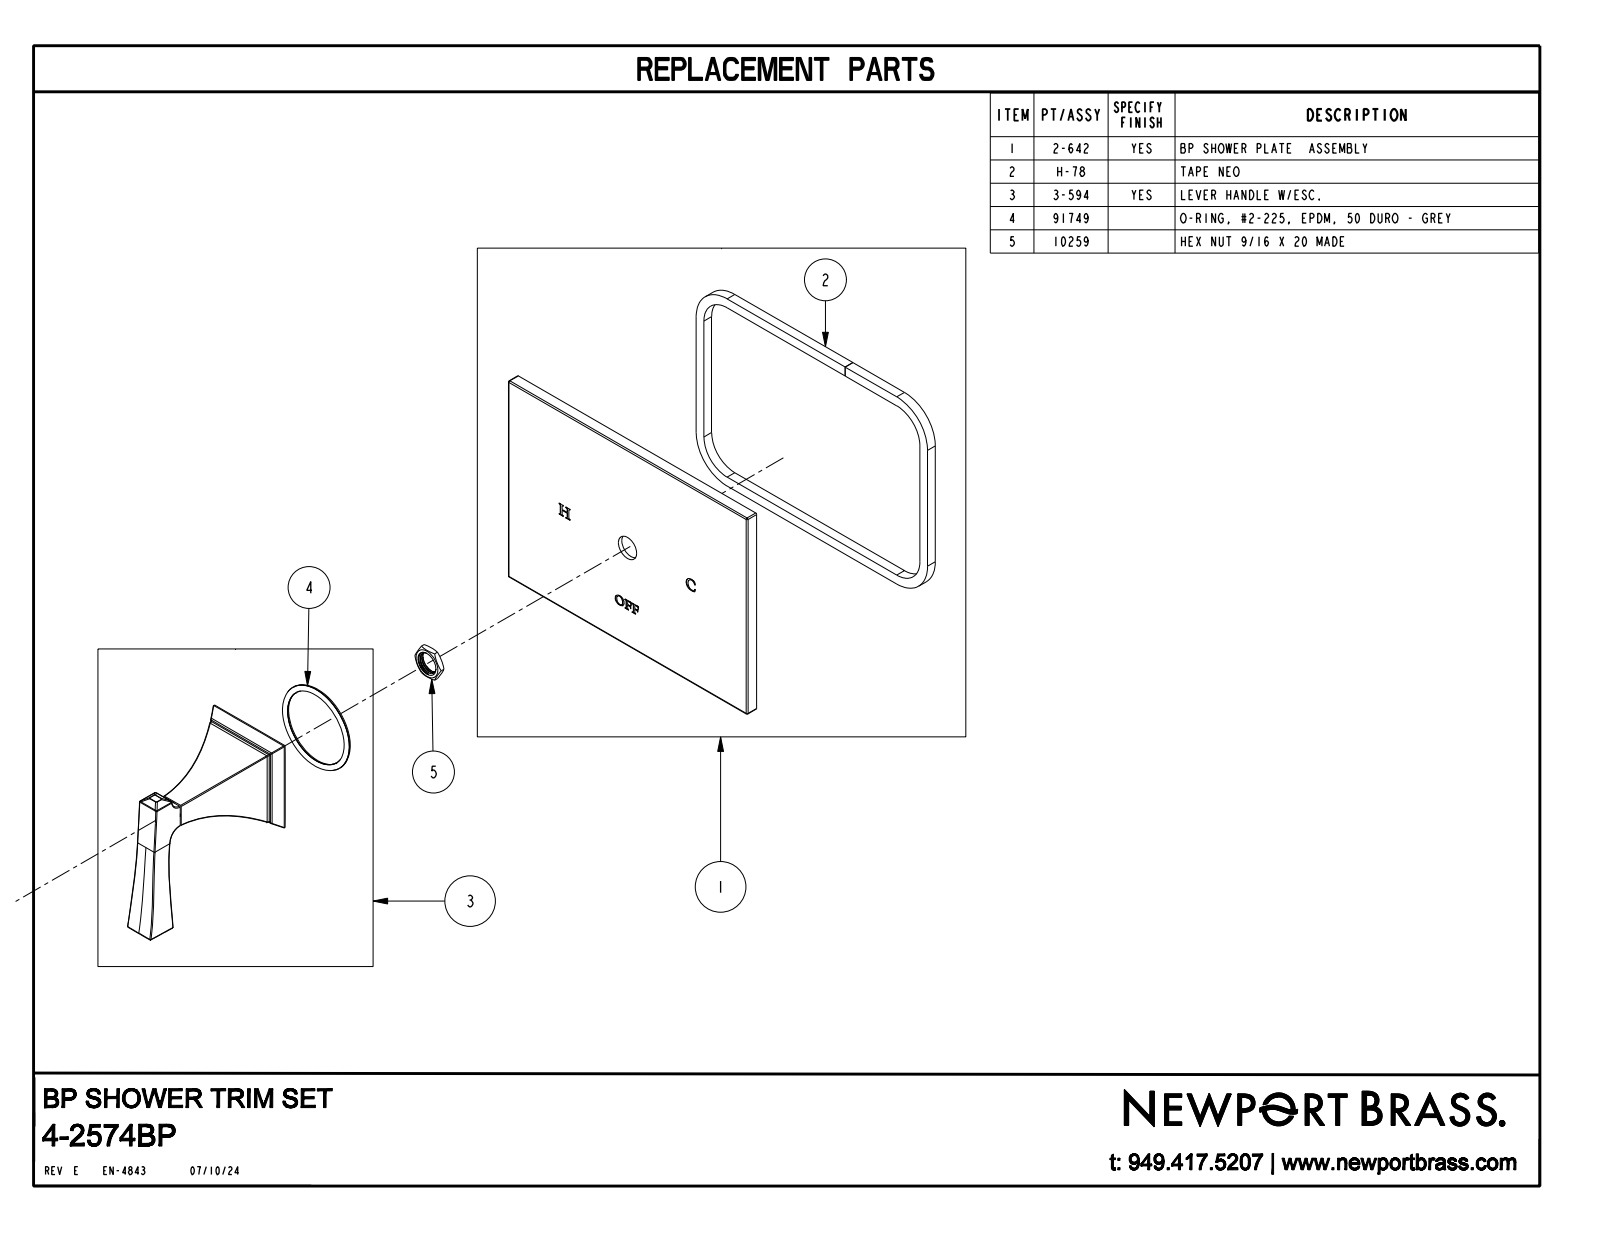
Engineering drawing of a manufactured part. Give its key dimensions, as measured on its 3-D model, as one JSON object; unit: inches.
{"part_name": "4-2574BP", "step_written_by": "CREO PARAMETRIC BY PTC INC, 2018400 (CONFIG_CONTROL_DESIGN)", "units": "inches", "bodies": {"solids": 1, "faces": 385, "planar": 60, "cylindrical": 34, "other": 291}, "overall_size": [7.75, 5.802, 3.904], "volume_in3": 18.69, "surface_area_in2": 110.3, "round_bosses_or_shafts": [[0.506, 1]], "partial_cylinders_radius": [[0.02, 16], [0.03, 8], [0.06, 8]], "face_to_face_distances": [0.31, 5.5, 7.75, 3.595, 4.155, 0.56, 0.295, 0.015, 2.809, 2.515]}
